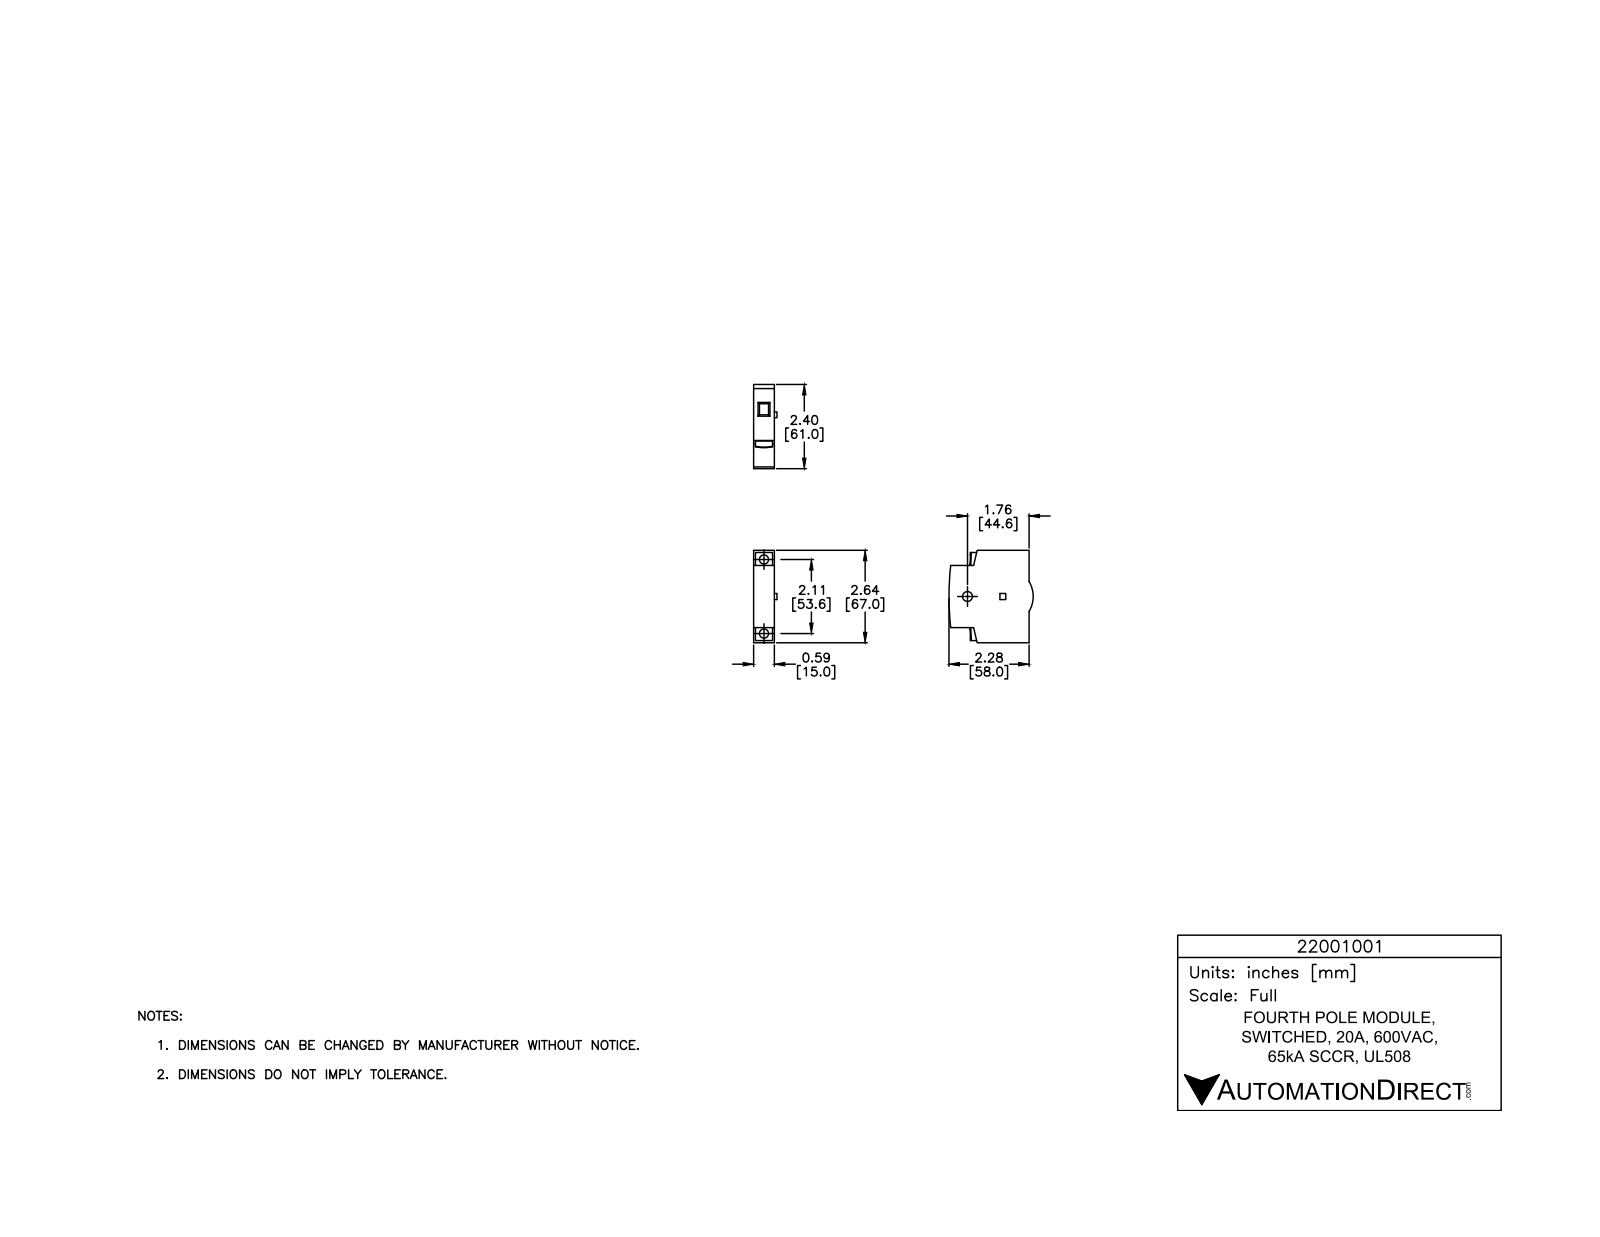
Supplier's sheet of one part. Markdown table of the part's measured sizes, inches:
| quantity | value |
| --- | --- |
| part name | 22001001-UL |
| STEP written by | SolidWorks 2021 (CONFIG_CONTROL_DESIGN) |
| units | inches |
| bodies | 1 solid, 61 faces (46 planar, 11 cylindrical, 4 other) |
| overall size | 2.638 × 2.402 × 0.665 |
| volume | 3.141 in³ |
| surface area | 18.13 in² |
| round holes (diameter × count) | 0.26 × 2, 0.283 × 1 |
| partial cylindrical surfaces (radius × count) | 0.827 × 1, 7.874 × 1 |
| main face-to-face distances | 0.591, 2.638, 0.433, 2.205, 1.772, 0.063, 2.575, 0.37, 2.142, 0.051 |
| hole center spacings | 2.11 |
